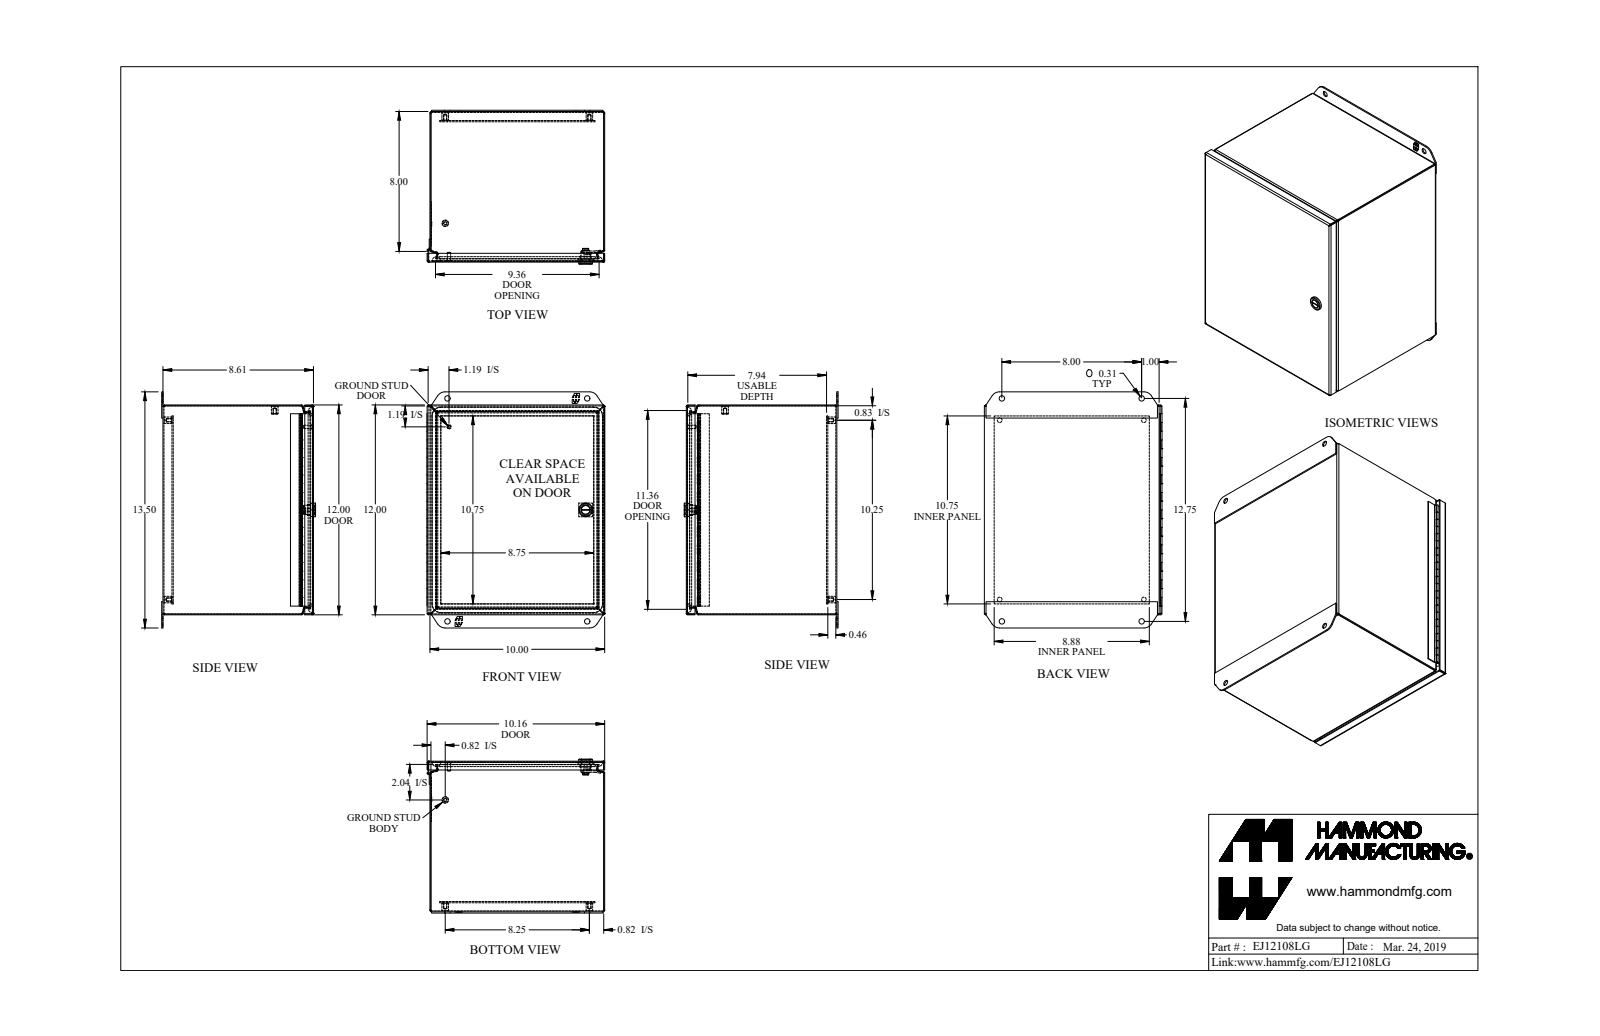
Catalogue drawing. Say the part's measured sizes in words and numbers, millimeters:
The part is named "EJ12108LG_Default". Its 3-D file was written by "SolidWorks 2019 (CONFIG_CONTROL_DESIGN)". It is 16 solids with 707 faces: 393 planar, 222 cylindrical and 92 other. Overall it measures 342.9 by 258.2 by 223.6 millimeters. Its volume is 820 500 cubic millimeters and its surface area 1 076 000 square millimeters. Round holes: 5 of diameter 4, 4 of diameter 6.7, 4 of diameter 8, 1 of diameter 1.3, 1 of diameter 13.1. Round bosses or shafts: 5 of diameter 9.5, 1 of diameter 20, 1 of diameter 13.6, 1 of diameter 12.6, 1 of diameter 11, 1 of diameter 6.4, 1 of diameter 4.8, 1 of diameter 2.5. Partial cylindrical surfaces (rounded edges, fillets, slot ends): 16 of radius 0.7, 16 of radius 2.2, 10 of radius 7.1, 4 of radius 6.4, 4 of radius 12.7, 4 of radius 12.7, 2 of radius 1.5, 2 of radius 13.7. The main face-to-face distances are 1.4, 217.3, 252.6, 303.4, 1.8, 15, 218.7, 215.8, 11.7, 13.1. The hole center spacings are 31.9, 292.1, 260.4, 208.8, 334.2, 357.7, 130.3, 162.
